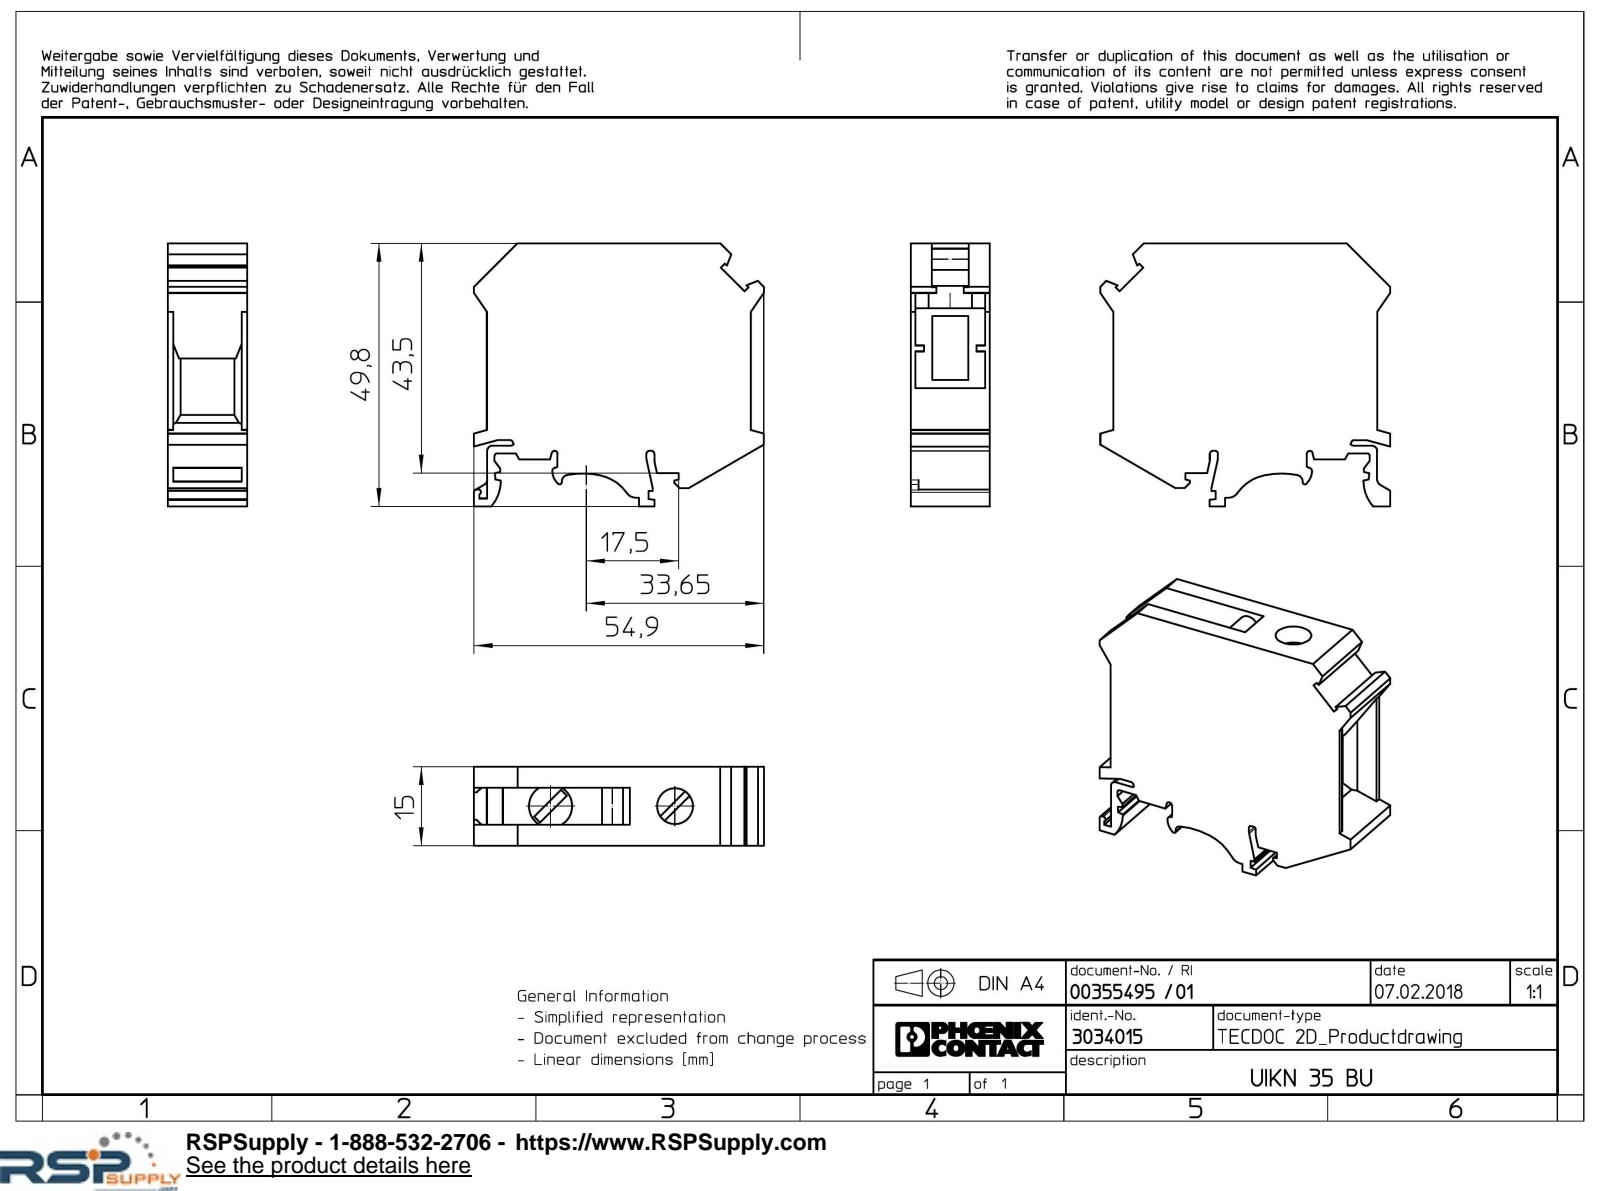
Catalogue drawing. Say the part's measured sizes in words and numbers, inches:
The part is named "UIKN_35_BU-select". Its 3-D file was written by "Creo Elements/Direct Modeling 20.1A 29-Sep-2018 (C) Parametric Technology GmbH (AUTOMOTIVE_DESIGN)". It is 1 solid with 158 faces: 128 planar, 30 cylindrical and 0 other. Overall it measures 2.161 by 1.961 by 0.591 inches. Its volume is 1.56 cubic inches and its surface area 16.89 square inches. Round holes: 1 of diameter 0.268. Round bosses or shafts: 1 of diameter 0.323, 1 of diameter 0.157. Partial cylindrical surfaces (rounded edges, fillets, slot ends): 8 of radius 0.02, 3 of radius 0.079, 2 of radius 0.039, 1 of radius 0.012, 1 of radius 0.016, 1 of radius 0.021, 1 of radius 0.028, 1 of radius 0.047. The main face-to-face distances are 0.591, 0.433, 0.157, 0.394, 0.118, 0.094, 0.496, 0.059, 0.339, 0.063.
